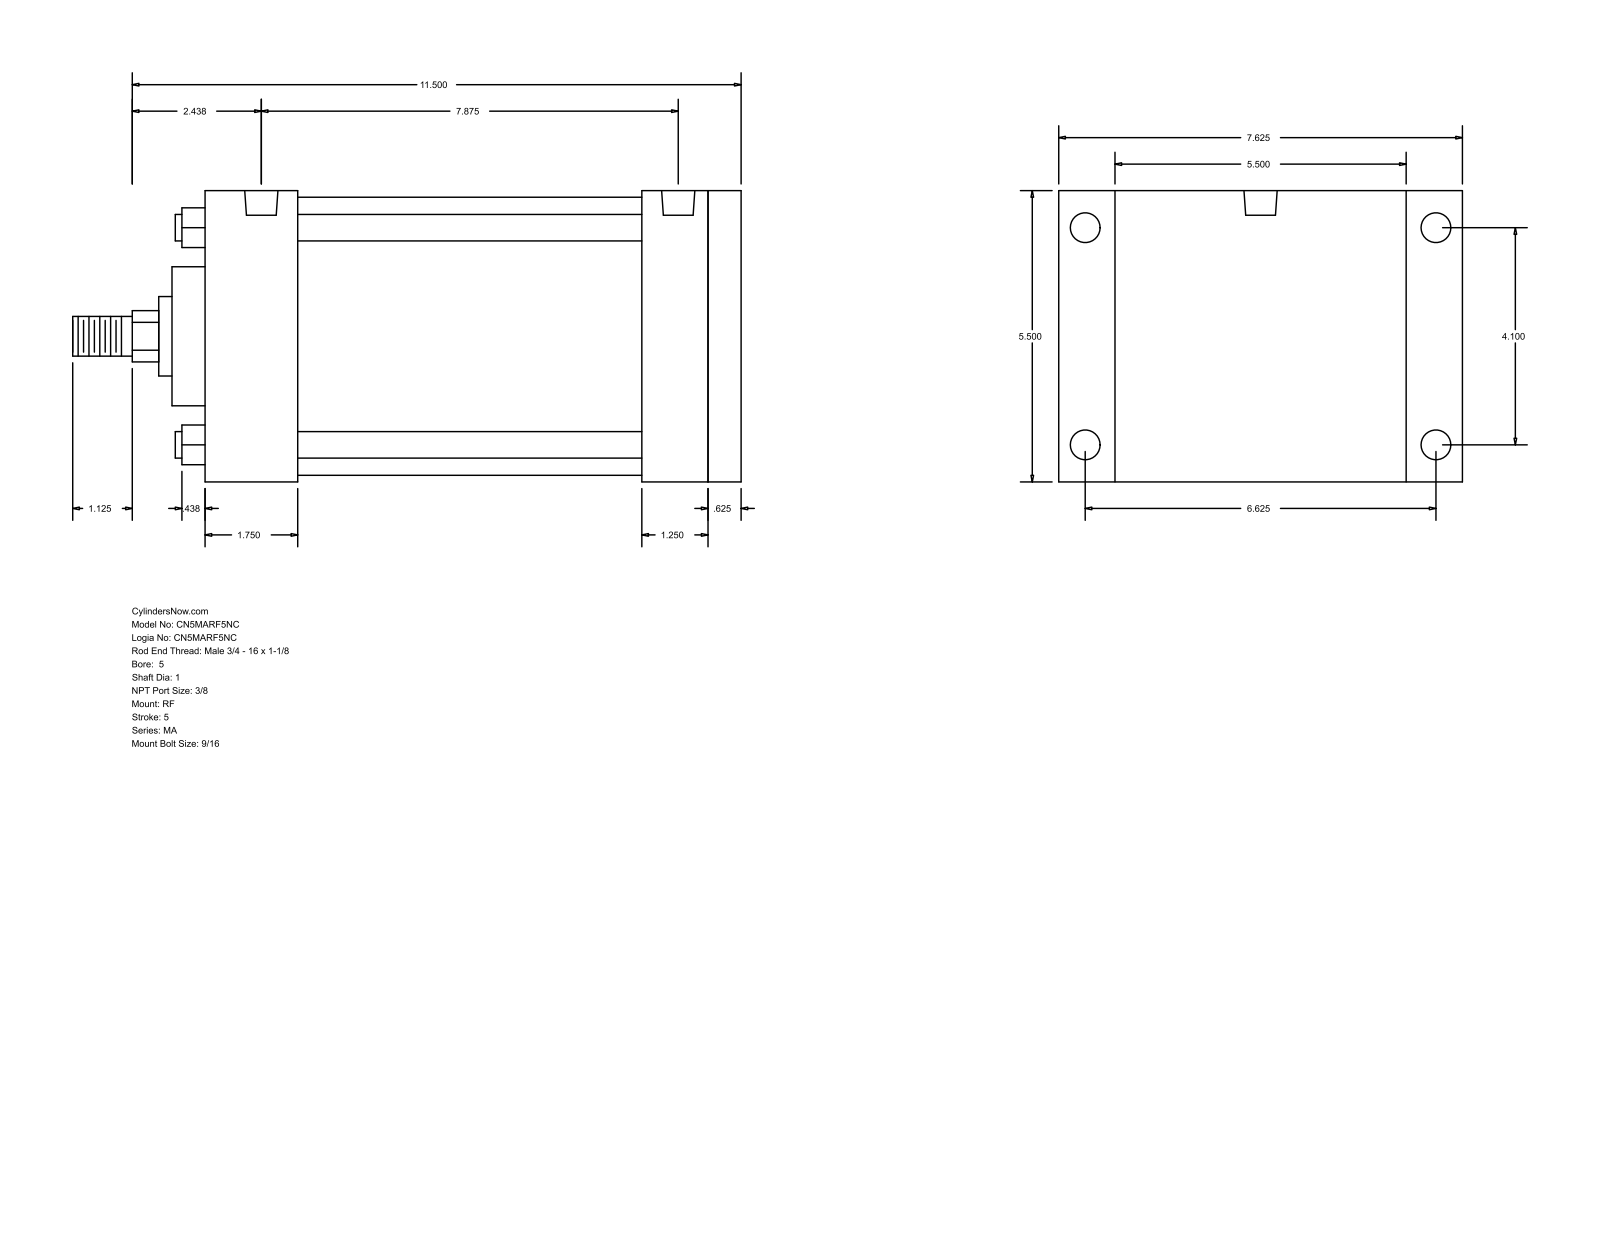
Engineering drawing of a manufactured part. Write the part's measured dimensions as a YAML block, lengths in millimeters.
part_name: "MA_RF__0500_1"
step_written_by: "GSSL Pune (CONFIG_CONTROL_DESIGN)"
units: millimeters
bodies: {solids: 0, faces: 94, planar: 65, cylindrical: 29, other: 0}
overall_size: [320.68, 193.68, 139.7]
round_holes:
  - {diameter: 11.11, count: 4}
  - {diameter: 14.29, count: 4}
  - {diameter: 15.93, count: 2}
round_bosses_or_shafts:
  - {diameter: 12.7, count: 4}
  - {diameter: 133.35, count: 1}
  - {diameter: 66.67, count: 1}
  - {diameter: 38.1, count: 1}
  - {diameter: 25.4, count: 1}
  - {diameter: 19.05, count: 1}
partial_cylinders:
  - {radius: 12.29, count: 1}
face_to_face_distances: [139.7, 257.18, 15.87, 241.31, 44.46, 196.85, 212.72, 209.55, 165.09, 31.76]
hole_center_spacings: [4.76, 104.14, 168.28, 190.51, 195.27, 197.9, 200.03]
